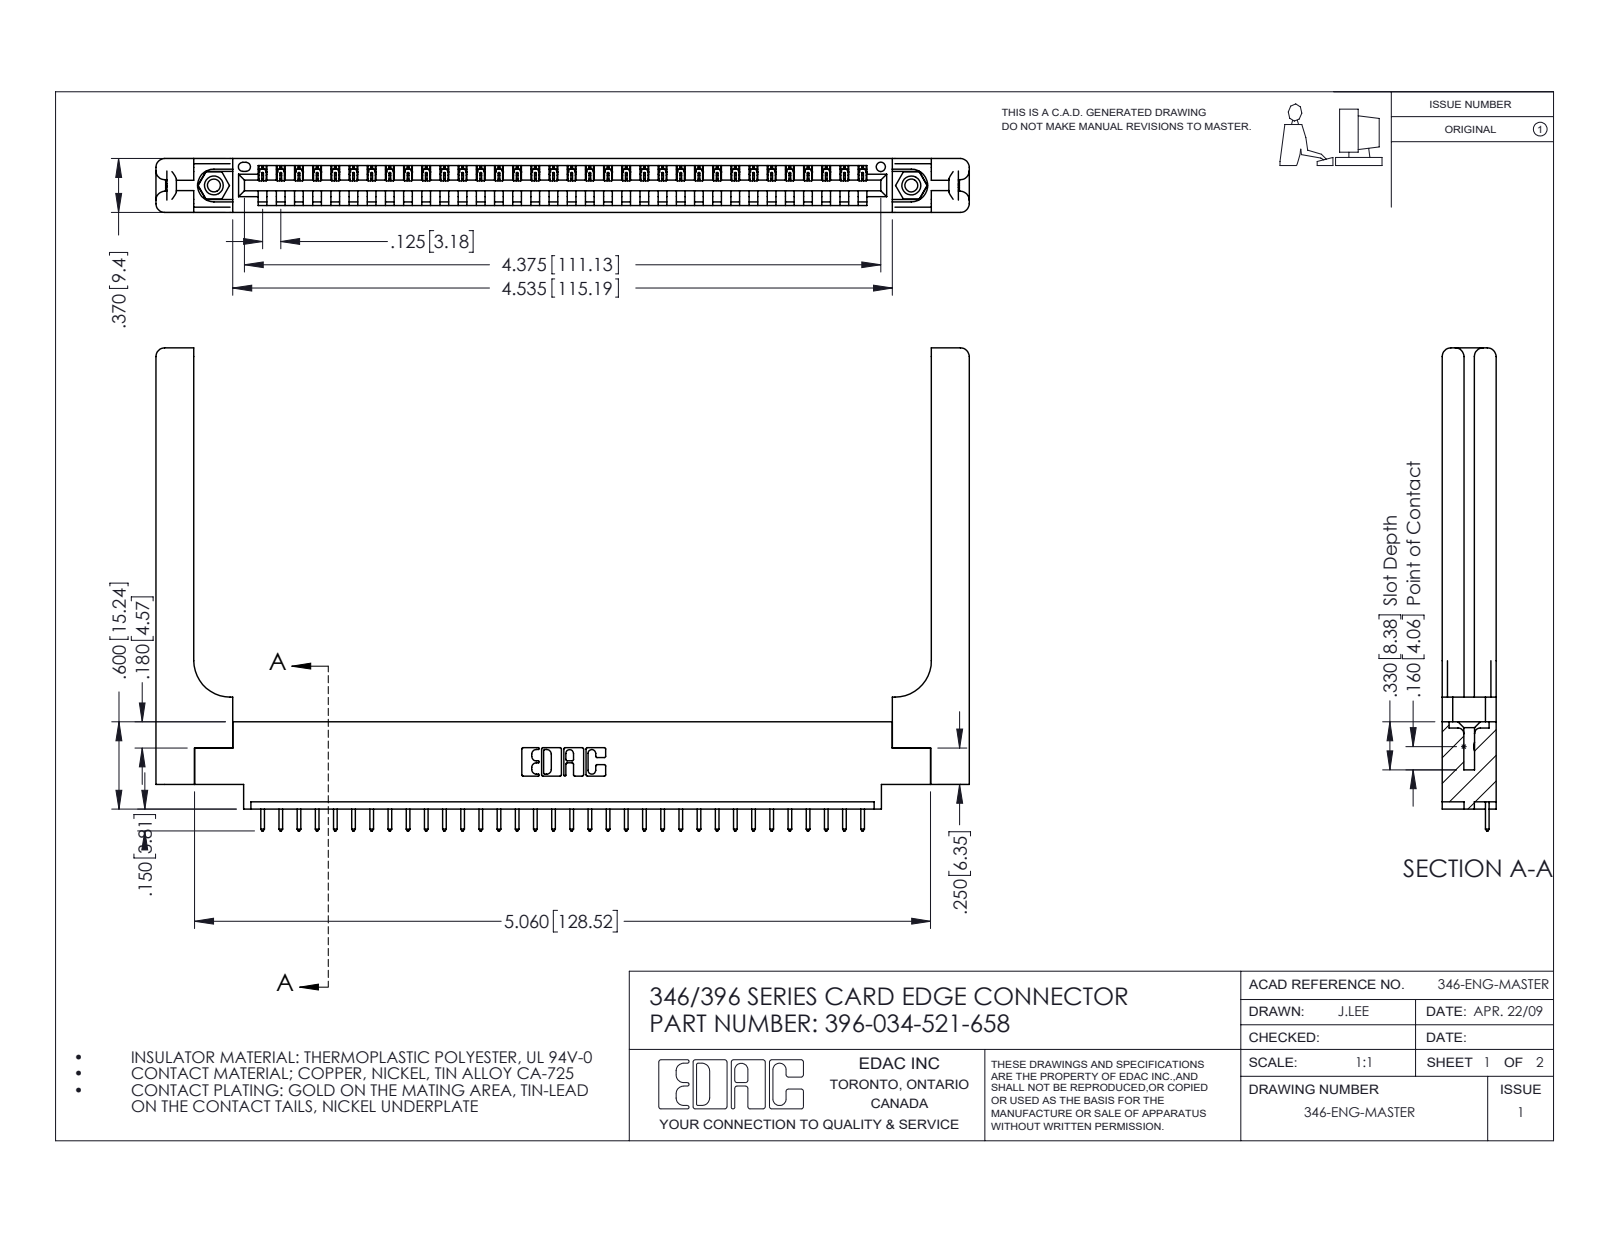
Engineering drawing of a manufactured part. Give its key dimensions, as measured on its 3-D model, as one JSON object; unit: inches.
{"part_name": "345-292-001_345-293-121; 346 Part_0.170 Offset - 0.156 Dia-TH; 396-034-521-658; 345-250-001_345-250-001-102 (+1 more)", "step_written_by": "SolidWorks 2016 (CONFIG_CONTROL_DESIGN)", "units": "inches", "bodies": {"solids": 39, "faces": 2354, "planar": 1588, "cylindrical": 706, "other": 60}, "overall_size": [5.591, 3.32, 0.37], "volume_in3": 1.27, "surface_area_in2": 33.27, "round_holes": [[0.089, 2], [0.125, 2], [0.156, 2], [0.064, 1]], "round_bosses_or_shafts": [[0.155, 2]], "partial_cylinders_radius": [[0.006, 68], [0.01, 68], [0.01, 22], [0.06, 16], [0.007, 6], [0.031, 6], [0.026, 3], [0.03, 2]], "face_to_face_distances": [0.37, 0.048, 0.322, 0.072, 0.148, 0.15, 0.25, 0.298, 0.025, 0.222], "hole_center_spacings": [0.246, 4.587, 4.795]}
